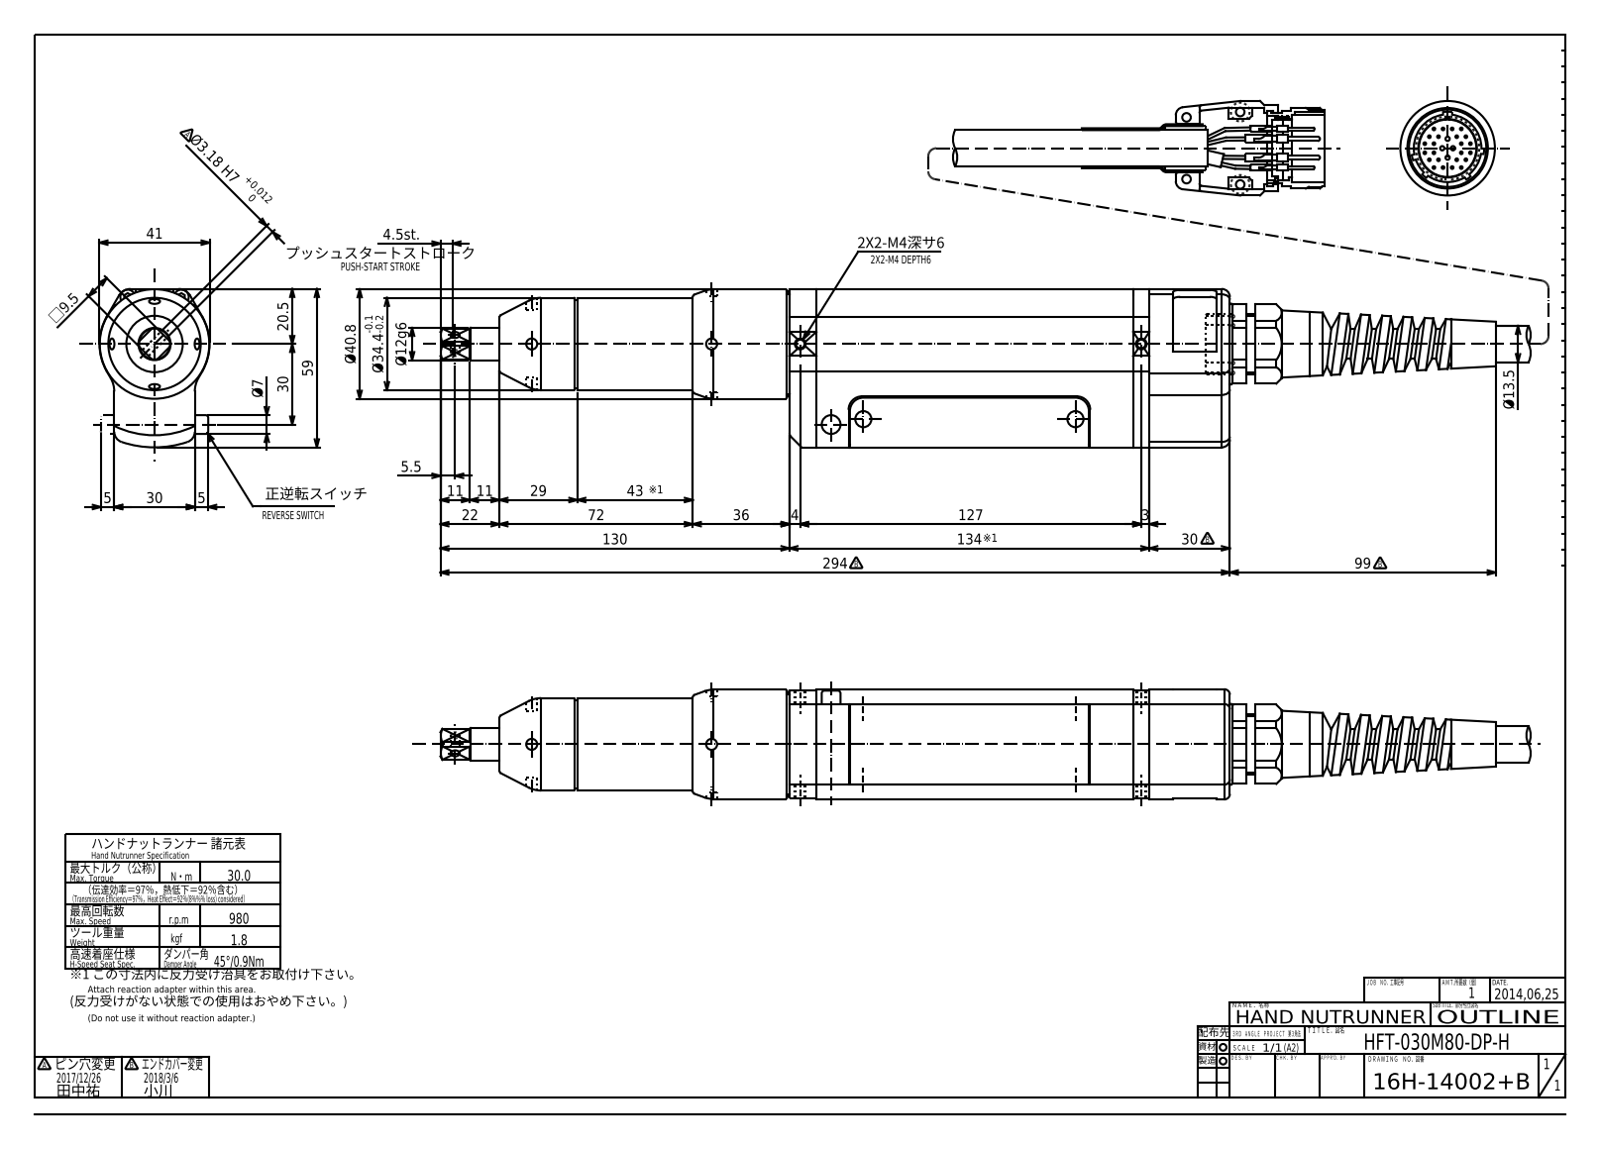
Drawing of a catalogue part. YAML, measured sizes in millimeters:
part_name: "HFT-030M80-DP-H(16H-14002+D)_OUTLINE_20241125"
step_written_by: "Autodesk Inventor 2023 (AUTOMOTIVE_DESIGN)"
units: millimeters
bodies: {solids: 1, faces: 714, planar: 383, cylindrical: 228, other: 103}
overall_size: [464.02, 59, 41]
volume: 458854
surface_area: 69518
round_holes:
  - {diameter: 3.4, count: 8}
  - {diameter: 4.1, count: 8}
  - {diameter: 2.46, count: 5}
  - {diameter: 3, count: 4}
  - {diameter: 3.1, count: 4}
  - {diameter: 6, count: 4}
  - {diameter: 3.3, count: 2}
  - {diameter: 6.5, count: 2}
  - {diameter: 6.6, count: 2}
  - {diameter: 3.18, count: 1}
  - {diameter: 4.2, count: 1}
  - {diameter: 7.5, count: 1}
round_bosses_or_shafts:
  - {diameter: 5.5, count: 8}
  - {diameter: 3, count: 4}
  - {diameter: 6, count: 2}
  - {diameter: 40.8, count: 1}
  - {diameter: 34.4, count: 1}
  - {diameter: 33, count: 1}
  - {diameter: 30, count: 1}
  - {diameter: 22.5, count: 1}
partial_cylinders:
  - {radius: 3, count: 8}
  - {radius: 5, count: 8}
  - {radius: 2, count: 7}
  - {radius: 0.5, count: 4}
  - {radius: 3.2, count: 4}
  - {radius: 4, count: 4}
  - {radius: 15, count: 2}
  - {radius: 2.5, count: 1}
face_to_face_distances: [30, 3.5, 4.5, 25.5, 29, 1, 24.5, 5, 21, 6]
hole_center_spacings: [15, 15.99, 8.08, 15.52, 21.21, 22.62, 26.85, 29.94]
